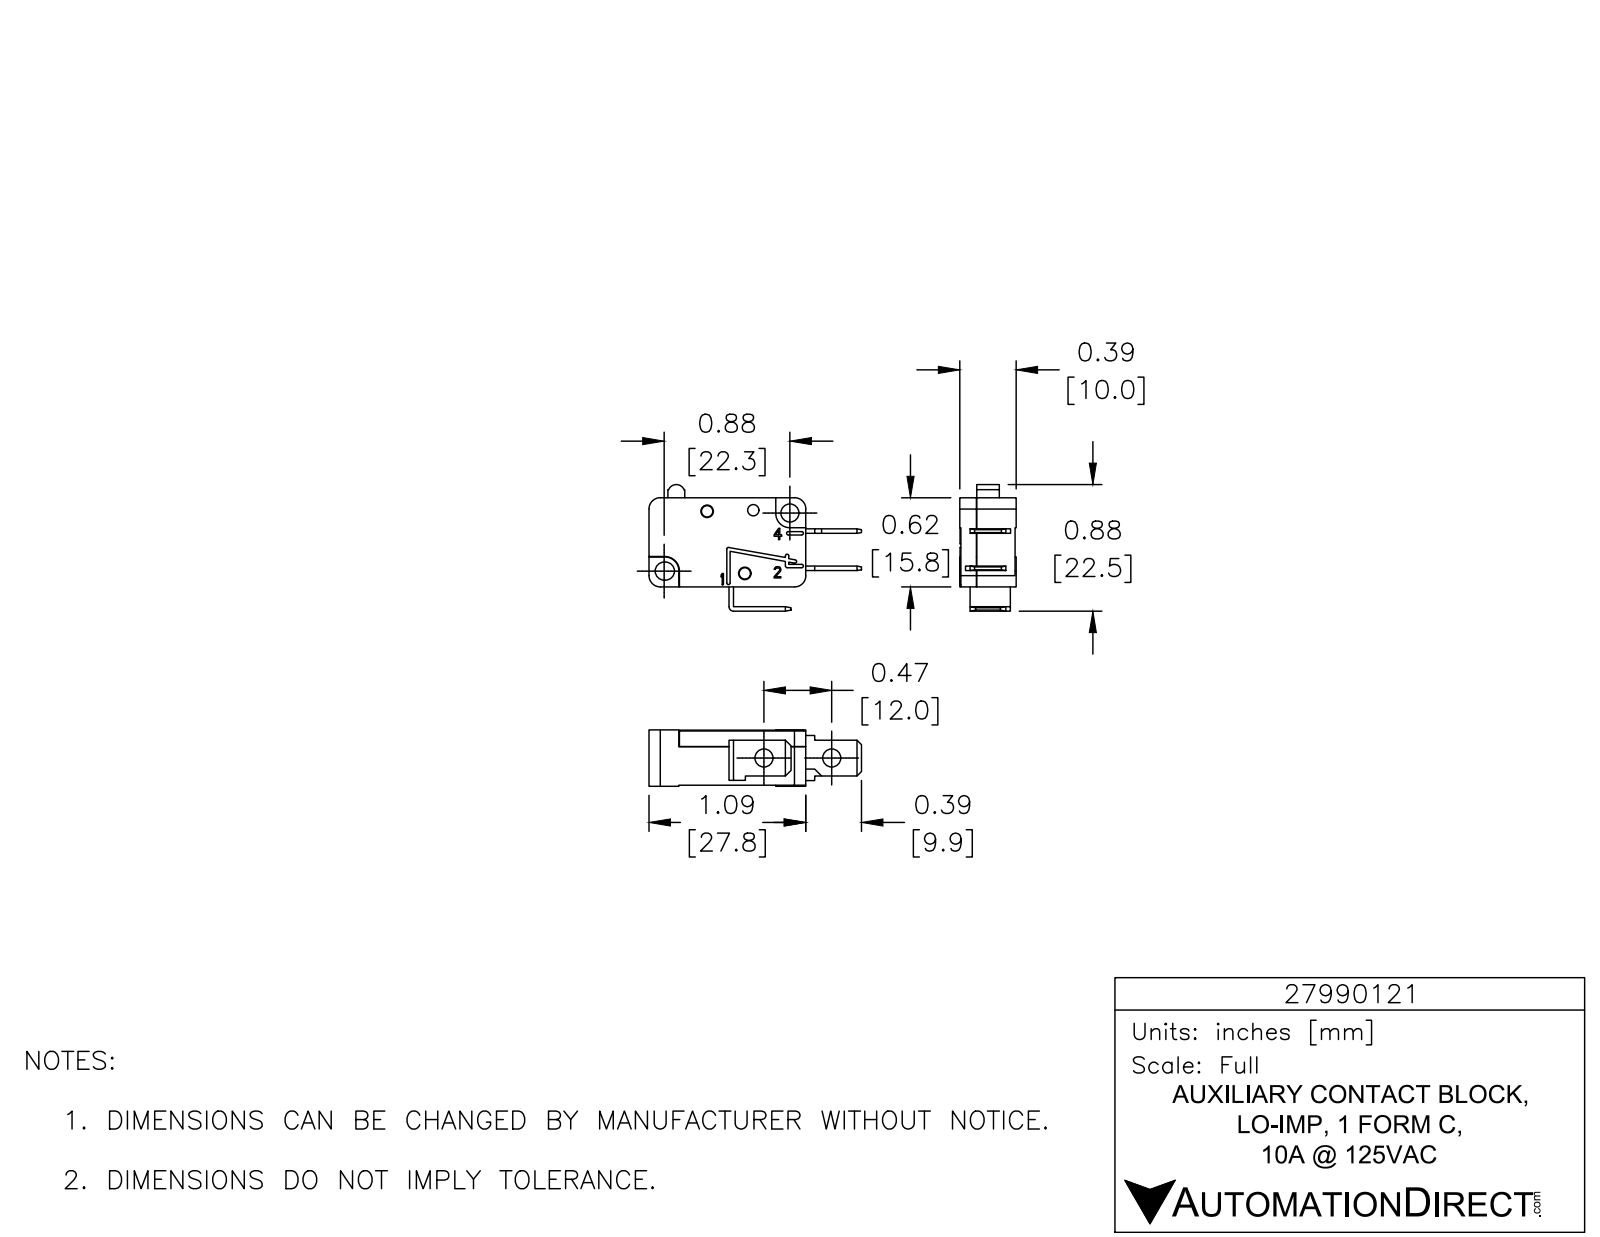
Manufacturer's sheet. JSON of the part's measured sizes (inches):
{"part_name": "27990121", "step_written_by": "SolidWorks 2015 (AUTOMOTIVE_DESIGN)", "units": "inches", "bodies": {"solids": 3, "faces": 337, "planar": 238, "cylindrical": 97, "other": 2}, "overall_size": [1.484, 0.884, 0.394], "volume_in3": 0.252, "surface_area_in2": 5.198, "round_holes": [[0.126, 3], [0.087, 2], [0.035, 1], [0.079, 1]], "round_bosses_or_shafts": [[0.079, 2], [0.069, 1]], "partial_cylinders_radius": [[0.012, 9], [0.021, 5], [0.079, 4], [0.017, 3], [0.008, 2], [0.009, 2], [0.01, 2], [0.025, 2]], "face_to_face_distances": [0.268, 0.27, 0.378, 0.11, 0.108, 0.622, 0.031, 1.094, 0.26, 0.543], "hole_center_spacings": [0.257, 0.29, 0.323, 0.445, 0.472, 0.507, 0.526, 0.579]}
